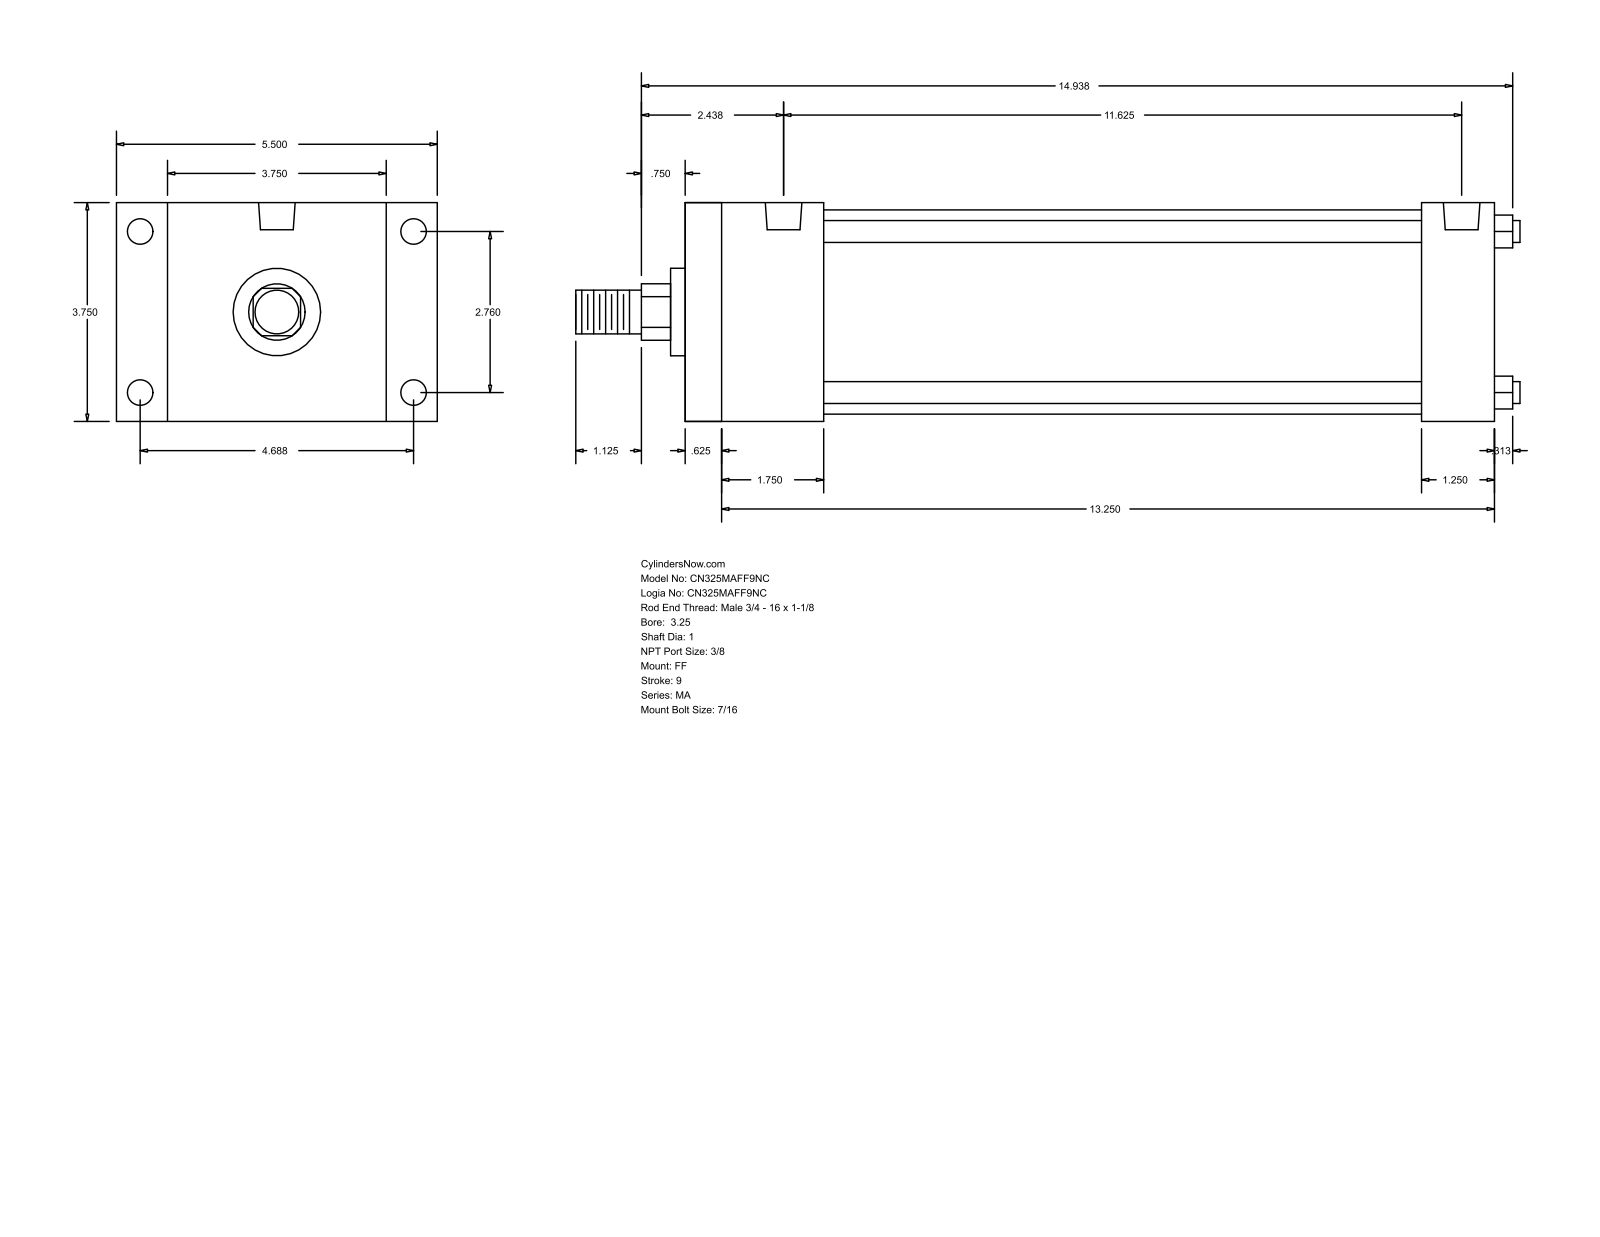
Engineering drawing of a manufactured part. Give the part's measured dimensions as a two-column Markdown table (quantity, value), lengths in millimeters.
| quantity | value |
| --- | --- |
| part name | MA_FF__0325_1 |
| STEP written by | GSSL Pune (CONFIG_CONTROL_DESIGN) |
| units | millimeters |
| bodies | 0 solids, 92 faces (64 planar, 28 cylindrical, 0 other) |
| overall size | 411.16 × 139.7 × 95.25 |
| round holes (diameter × count) | 11.11 × 8, 15.93 × 2 |
| round bosses / shafts (diameter × count) | 9.53 × 4, 88.9 × 1, 38.1 × 1, 25.4 × 1, 19.05 × 1 |
| partial cylindrical surfaces (radius × count) | 12.29 × 1 |
| main face-to-face distances | 95.24, 352.43, 15.87, 336.56, 22.23, 117.47, 60.33, 320.68, 44.46, 304.81 |
| hole center spacings | 4.76, 70.1, 119.06, 138.16, 285.76, 290.52, 295.28 |
